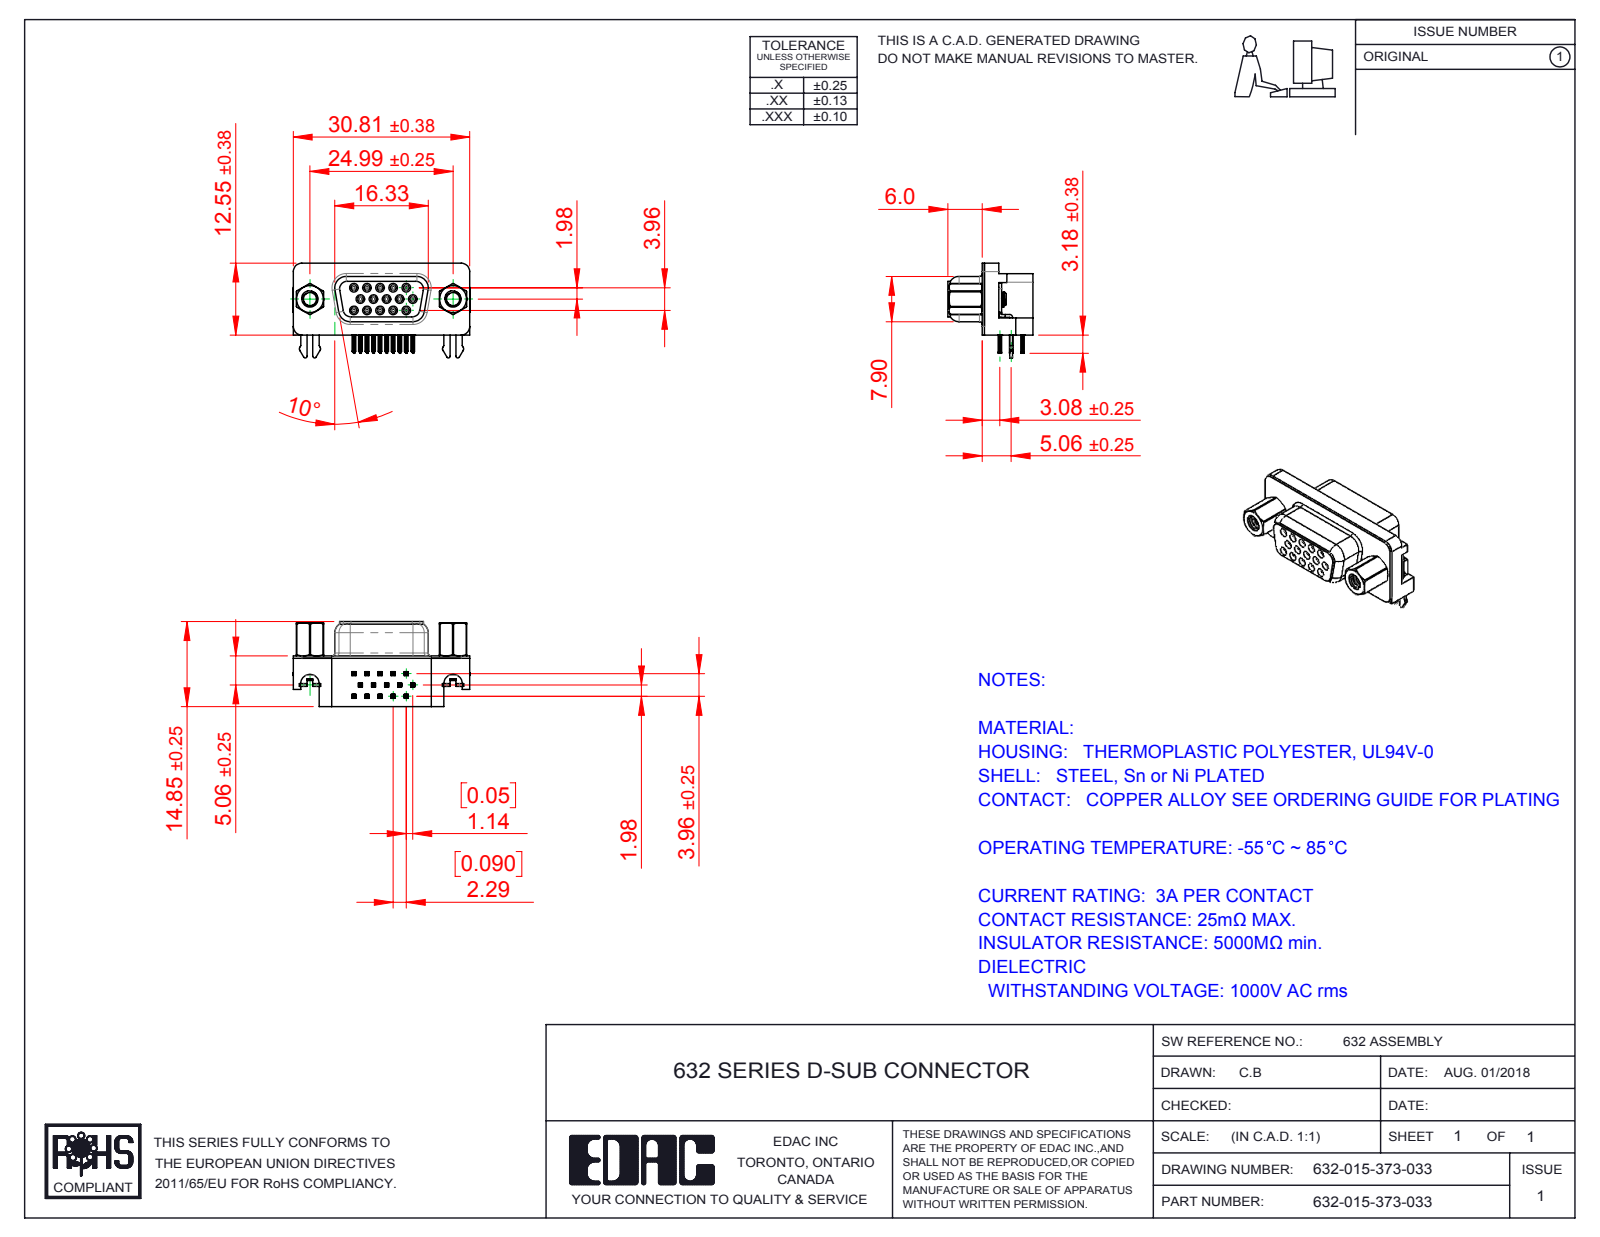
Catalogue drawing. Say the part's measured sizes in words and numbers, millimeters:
The part is named "632 Contact Top; 632-015-373-003; 632 Housing_15 Socket; 632 Contact Bottom (+5 more)". Its 3-D file was written by "SolidWorks 2016 (CONFIG_CONTROL_DESIGN)". It is 21 solids with 2376 faces: 996 planar, 646 cylindrical and 734 other. Overall it measures 30.89 by 16.55 by 14.85 millimeters. Its volume is 3 051 cubic millimeters and its surface area 5 177 square millimeters. Round holes: 15 of diameter 0.8, 15 of diameter 0.9, 2 of diameter 2.29, 2 of diameter 4, 2 of diameter 4.8, 2 of diameter 5. Round bosses or shafts: 15 of diameter 1.2, 2 of diameter 4.9, 2 of diameter 2.79. Partial cylindrical surfaces (rounded edges, fillets, slot ends): 120 of radius 0.1, 60 of radius 0.15, 30 of radius 0.35, 15 of radius 0.34, 11 of radius 1, 10 of radius 0.28, 10 of radius 0.5, 8 of radius 1.35. The main face-to-face distances are 0.4, 1.98, 8.45, 8.85, 2.9, 2.5, 5.95, 6.7, 7.05, 3.17. The hole center spacings are 2.28, 2.29, 3.96, 4.57, 6.05, 3.97, 4.58, 6.86.
